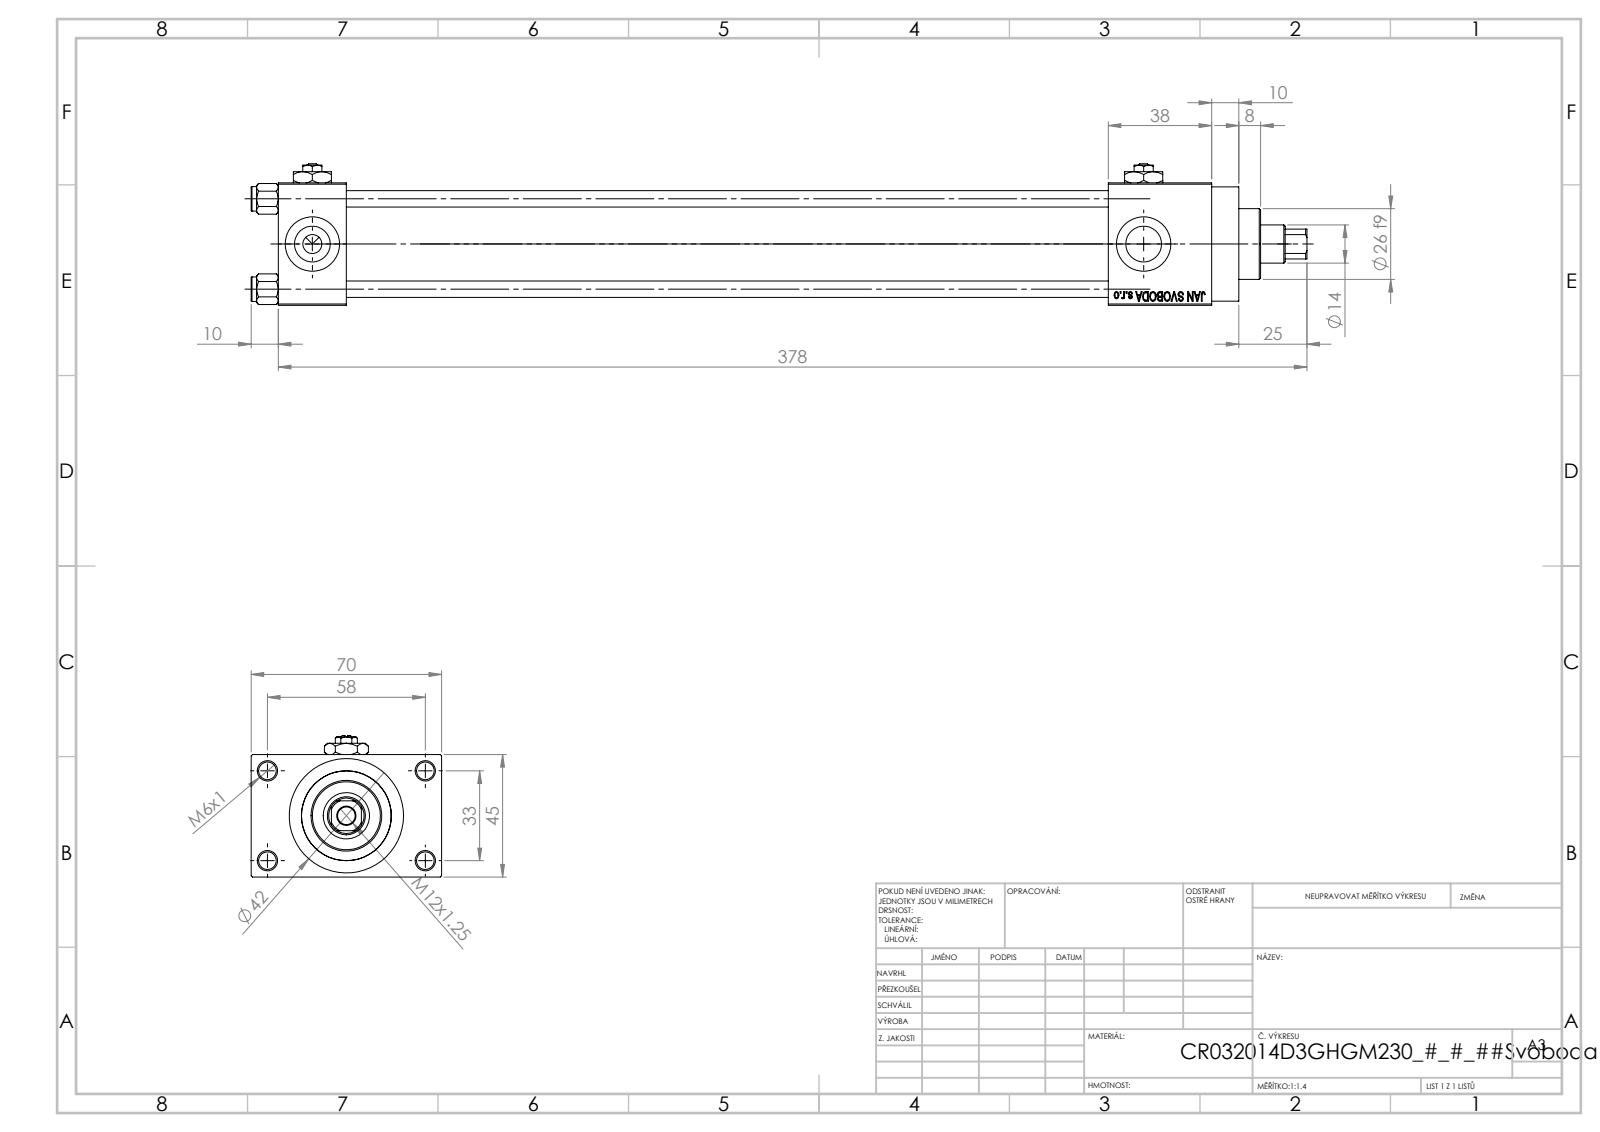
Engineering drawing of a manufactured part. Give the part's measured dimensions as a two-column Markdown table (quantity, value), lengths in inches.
| quantity | value |
| --- | --- |
| part name | Zatka_pro_OIL_PORT; V215CR_D_Body; V215CR_D_TYCINKA; V215_VC_A (+2 more) |
| STEP written by | SolidWorks 2019 (CONFIG_CONTROL_DESIGN) |
| units | inches |
| bodies | 13 solids, 1201 faces (542 planar, 99 cylindrical, 560 other) |
| overall size | 15.276 × 2.756 × 2.047 |
| volume | 22.36 in³ |
| surface area | 240.5 in² |
| round holes (diameter × count) | 0.256 × 5, 0.236 × 4, 0.518 × 4, 0.787 × 4, 0.276 × 3, 0.551 × 1, 0.669 × 1, 0.945 × 1, 1.26 × 1, 1.299 × 1 |
| round bosses / shafts (diameter × count) | 0.354 × 4, 1.654 × 1, 1.496 × 1, 1.024 × 1 |
| partial cylindrical surfaces (radius × count) | 0.256 × 1 |
| main face-to-face distances | 1.772, 0.984, 0.492, 11.024, 12.008, 2.264, 12.52, 1.496, 13.504, 2.756 |
| hole center spacings | 0.488, 0.924, 1.307, 1.314, 1.392, 1.795, 2.219, 1.299 |
